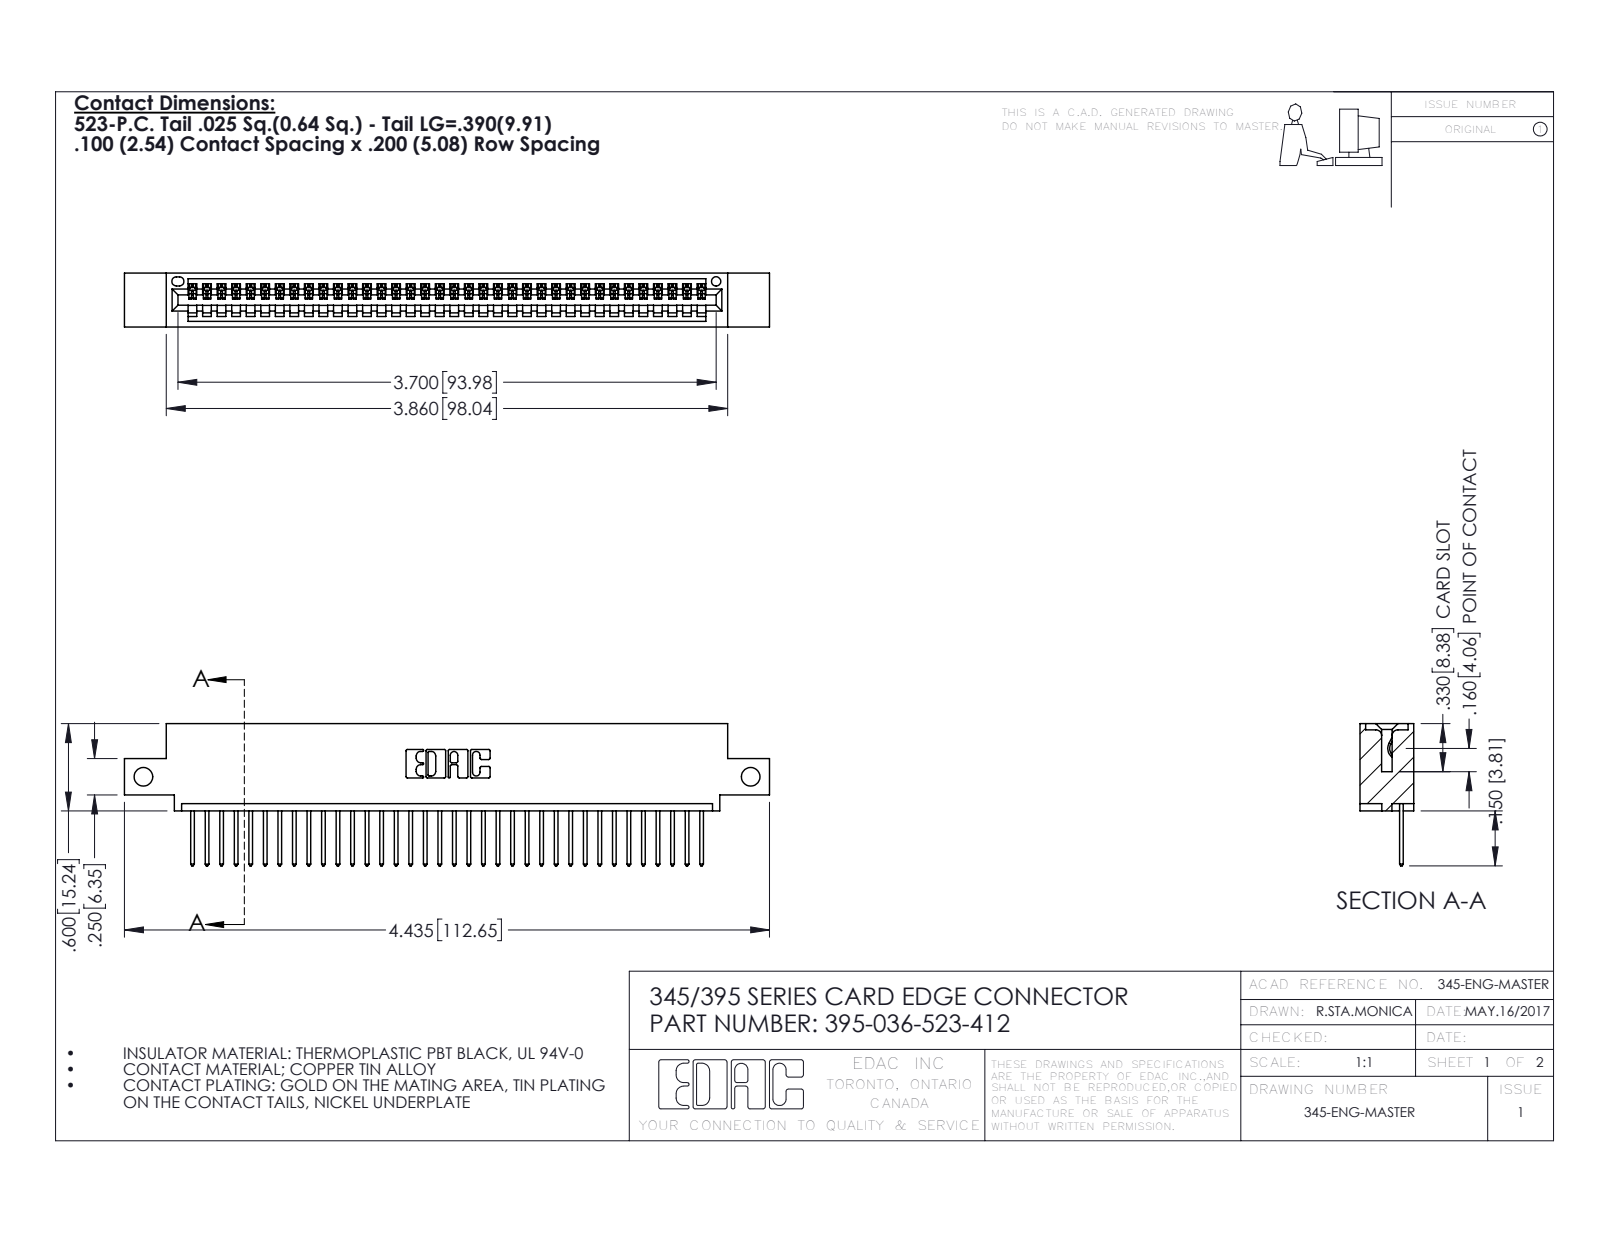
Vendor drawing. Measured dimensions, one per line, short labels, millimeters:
name: 395-036-523-412; 345-292-001_345-293-123; 345 Part_0.110 Offset - Side Mount
written by: SolidWorks 2016 (CONFIG_CONTROL_DESIGN)
unit: mm
bodies: 37 solids, 2218 faces (1524 planar, 694 cylindrical, 0 other)
size: 112.6 × 24.8 × 9.4
volume: 10 500 mm³; area: 13 820 mm²
holes: 2× ⌀3.3, 1× ⌀1.6
rounds: 72× R0.2, 72× R0.3, 22× R0.3, 6× R0.2, 6× R0.8, 3× R0.7, 2× R0.8, 2× R1
face distances: 7.6, 1.8, 9.4, 5.1, 2.5, 6.9, 0.6, 5.7, 3.8, 1.8
hole spacings: 106
